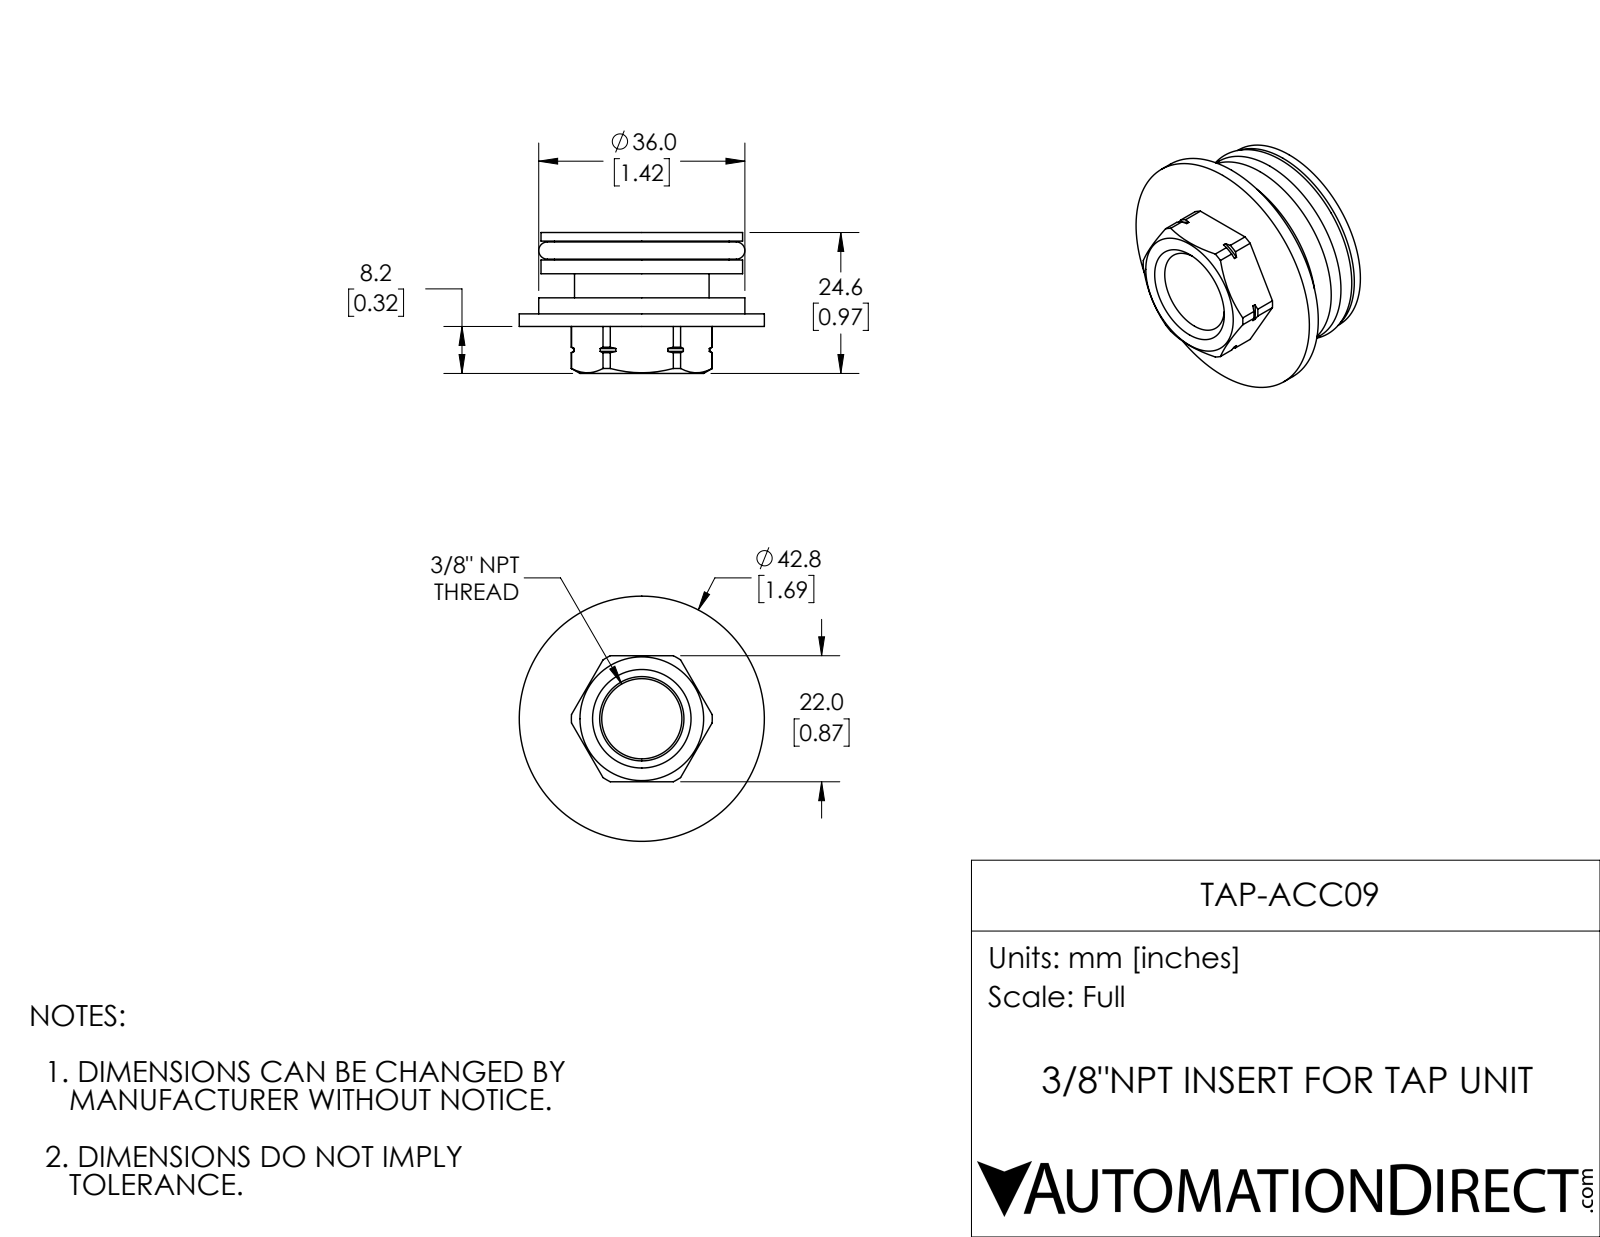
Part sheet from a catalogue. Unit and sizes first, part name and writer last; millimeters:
Units: millimetres
Overall size (bounding box): 42.8 × 42.8 × 24.6
Round holes (diameter × count): ⌀14 ×1, ⌀26 ×1
Round bosses / shafts (diameter × count): ⌀42.8 ×1, ⌀36 ×1, ⌀35.2 ×1, ⌀30.5 ×1, ⌀23.5 ×1
Partial cylindrical surfaces — rounded edges, fillets, slot ends (radius × count): R11.9 ×1, R12.3 ×1
Main face-to-face distances: 5, 9.2, 4.2, 16.4, 11.4, 7.2, 2.2, 2.8, 7, 14.2
Volume: 12 400 mm³ · Surface area: 8 071 mm²
Bodies: 1 solid, 75 faces (14 planar, 36 cylindrical, 25 other)
Part name (STEP PRODUCT): TAP-ACC09
STEP written by: SolidWorks 2017 (AUTOMOTIVE_DESIGN)
